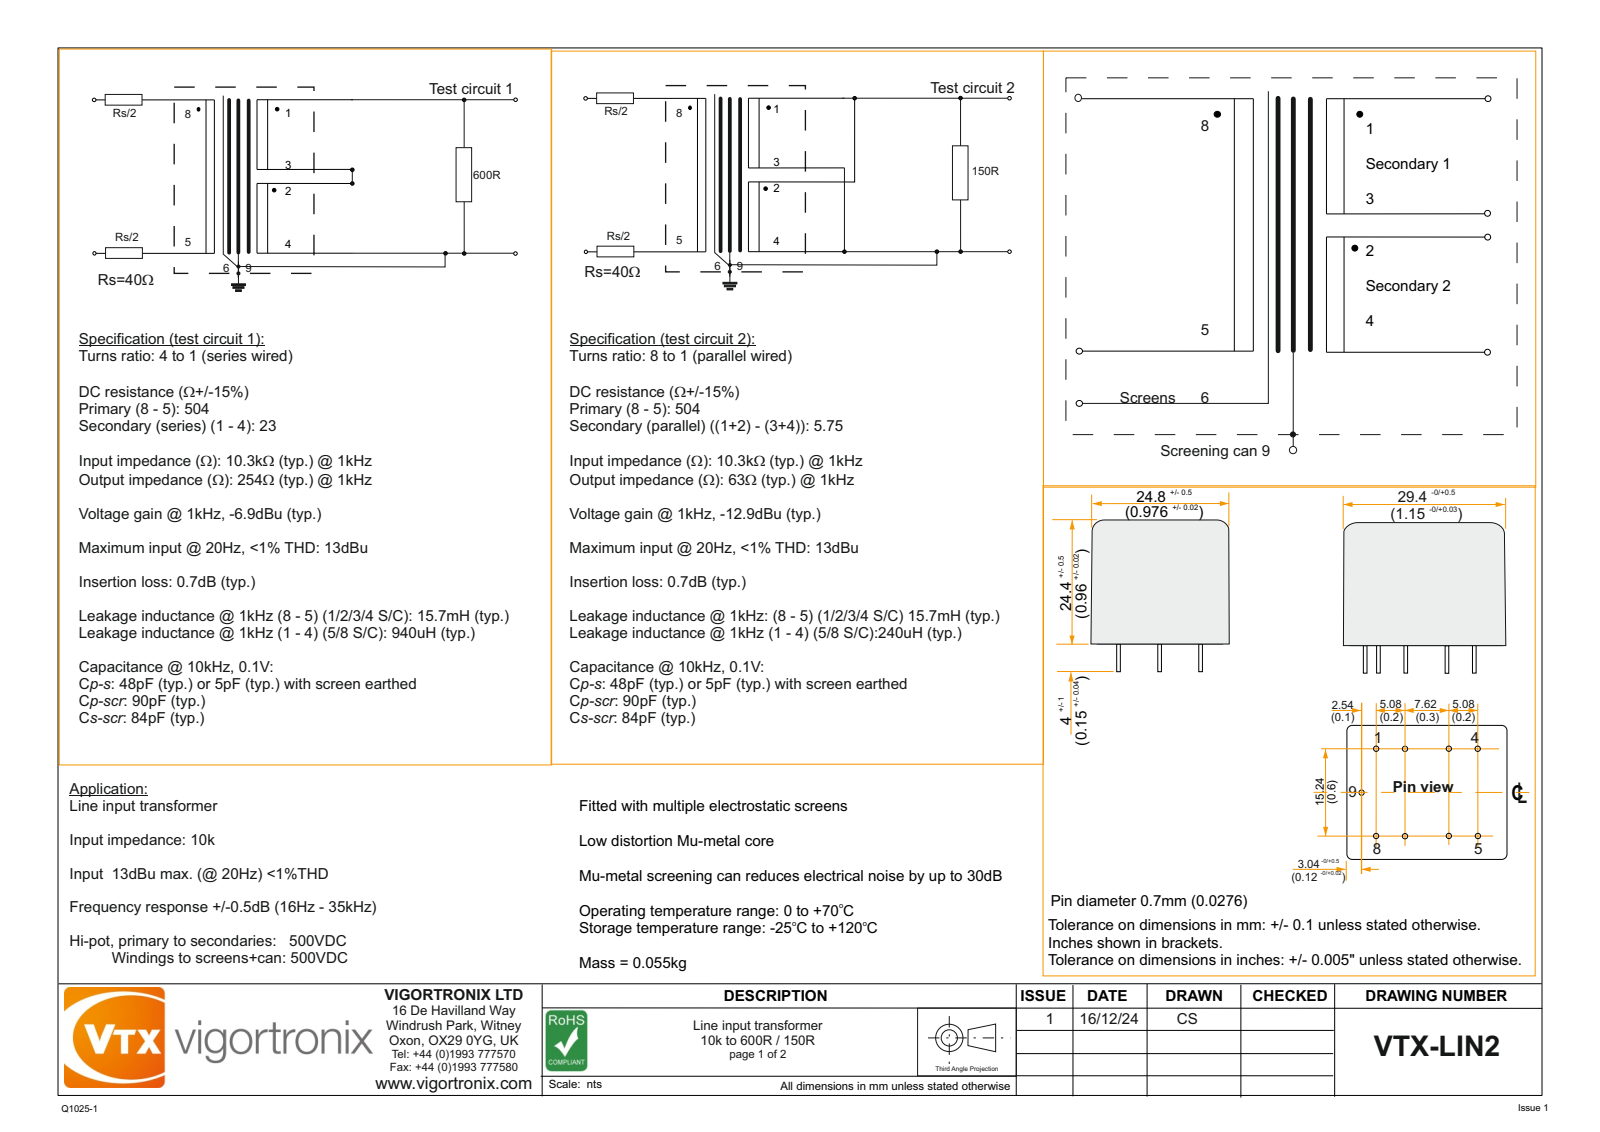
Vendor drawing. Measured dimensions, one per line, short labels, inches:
name: VTX-LIN2 LID; VTX-LIN2; VTX-LIN2 BOBBIN; VTX-LIN2 CAN
written by: SolidWorks 2024 (AUTOMOTIVE_DESIGN)
unit: in
bodies: 3 solids, 130 faces (36 planar, 74 cylindrical, 20 other)
size: 1.166 × 1.126 × 0.993
volume: 0.935 in³; area: 16.83 in²
holes: 8× ⌀0.138, 1× ⌀0.059
bosses: 8× ⌀0.028
rounds: 20× R0.02, 8× R0.075, 8× R0.098, 4× R0.079
face distances: 0.024, 0.921, 0.898, 0.886, 0.035, 0.909, 0.945, 0.906, 1.083, 0.102
hole spacings: 0.2, 0.5, 0.6, 0.632, 0.671, 0.781, 0.3, 0.316
